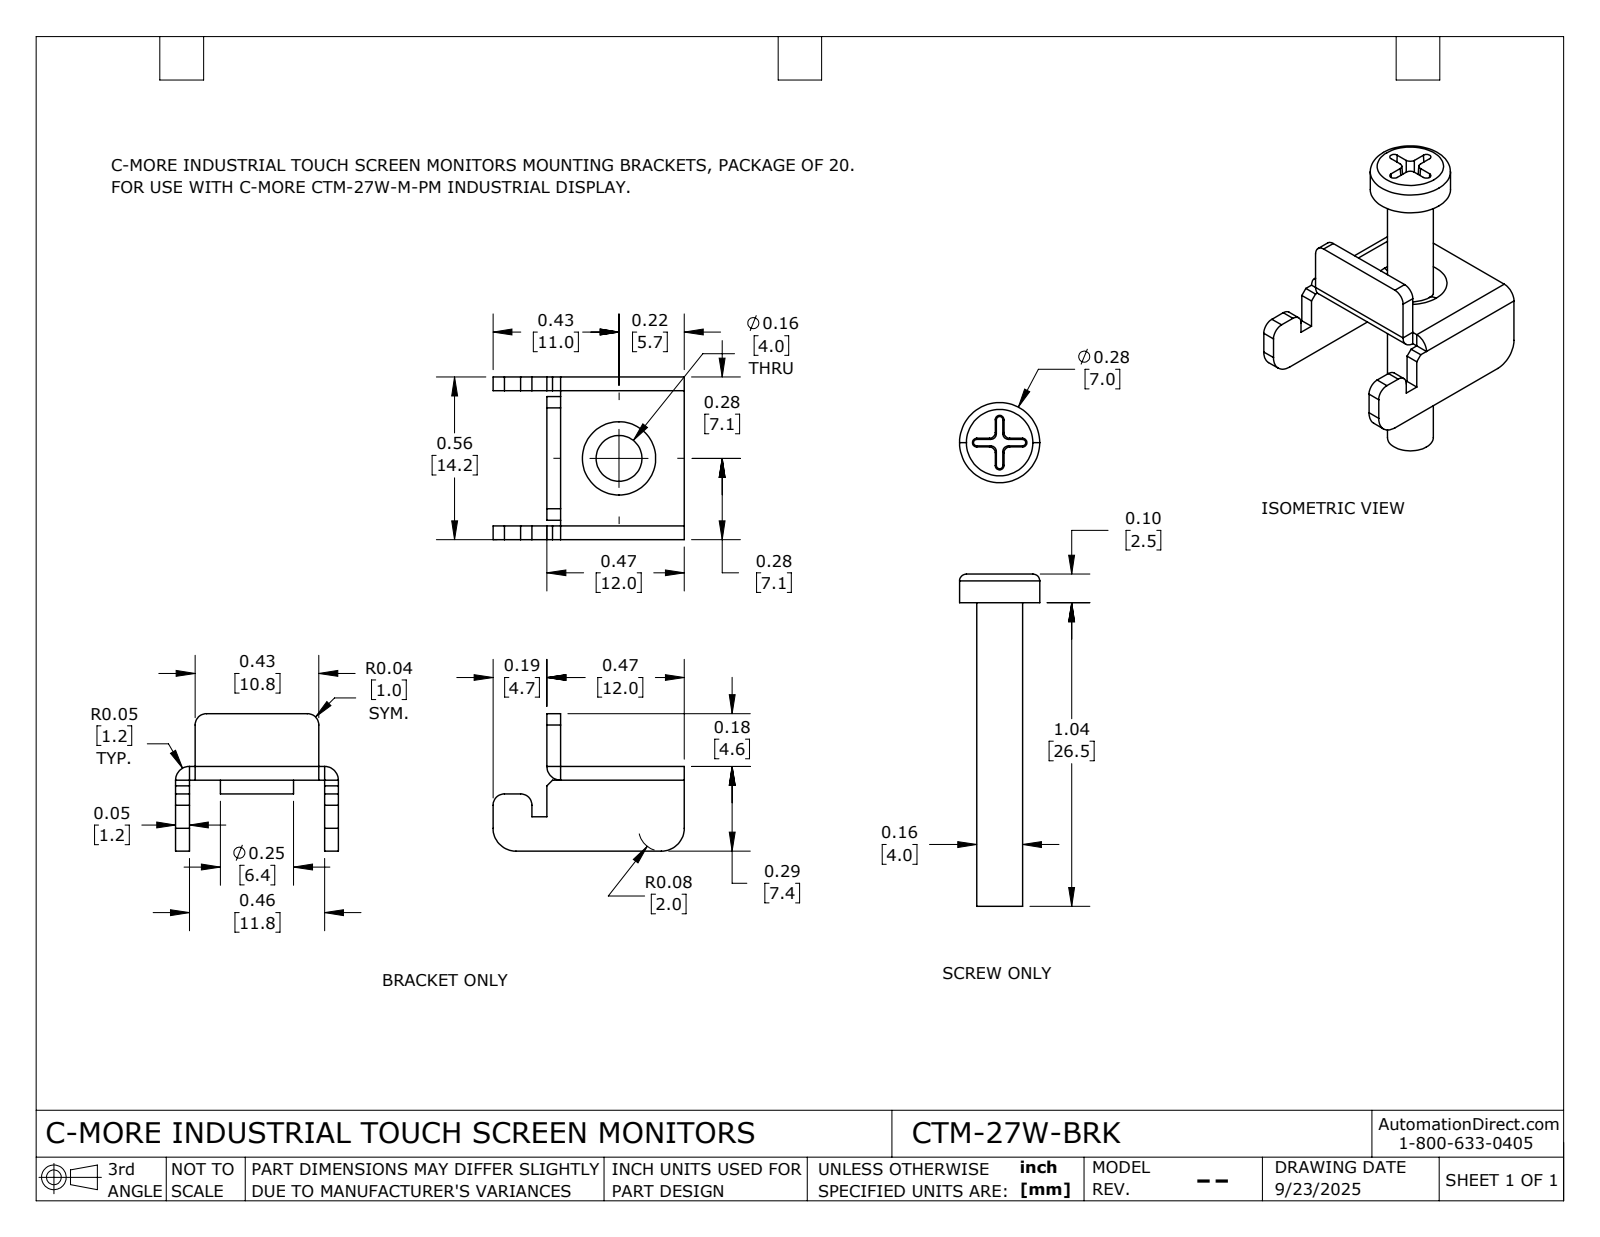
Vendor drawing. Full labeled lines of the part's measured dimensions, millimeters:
Part name (STEP PRODUCT): clip_om_sp2-20241226
STEP written by: SolidWorks 2024 (AUTOMOTIVE_DESIGN)
Units: millimetres
Bodies: 2 solids, 85 faces (52 planar, 25 cylindrical, 8 other)
Overall size (bounding box): 29 × 16.7 × 14.2
Volume: 880 mm³ · Surface area: 1 431 mm²
Round holes (diameter × count): ⌀4 ×1
Round bosses / shafts (diameter × count): ⌀7 ×1, ⌀6.4 ×1
Partial cylindrical surfaces — rounded edges, fillets, slot ends (radius × count): R0.5 ×4, R1 ×4, R1.2 ×3, R2 ×2
Main face-to-face distances: 1.2, 13, 11.8, 14.2, 12, 10.8, 12.5, 6.2, 7.4, 17.4
